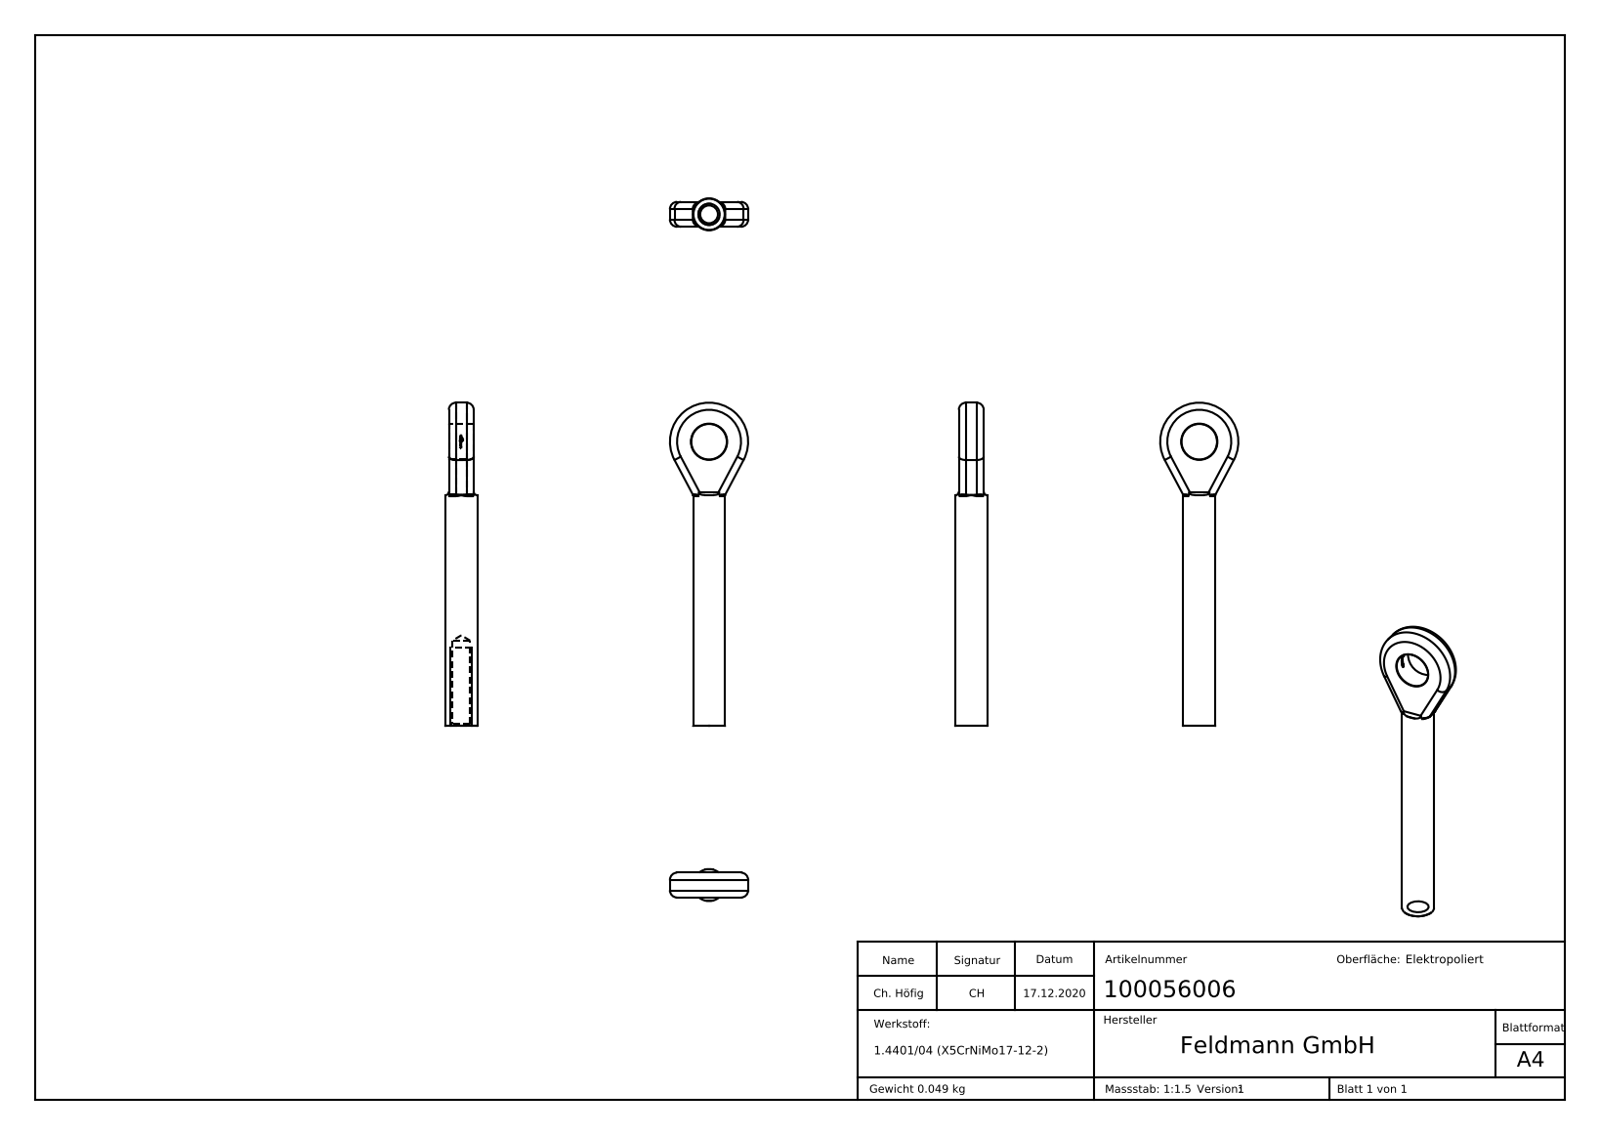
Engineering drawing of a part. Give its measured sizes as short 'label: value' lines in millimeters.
name: 100056006
written by: SolidWorks 2018 (CONFIG_CONTROL_DESIGN)
unit: mm
bodies: 1 solid, 336 faces (99 planar, 44 cylindrical, 193 other)
size: 91 × 22 × 9
volume: 6 064 mm³; area: 3 579 mm²
holes: 1× ⌀5, 1× ⌀10
bosses: 1× ⌀9
rounds: 4× R2, 2× R0.85, 1× R5.1, 1× R11
face distances: 7, 65, 3.14, 3.86, 0.72, 0.36, 0.42, 3.26, 3.74, 0.6
